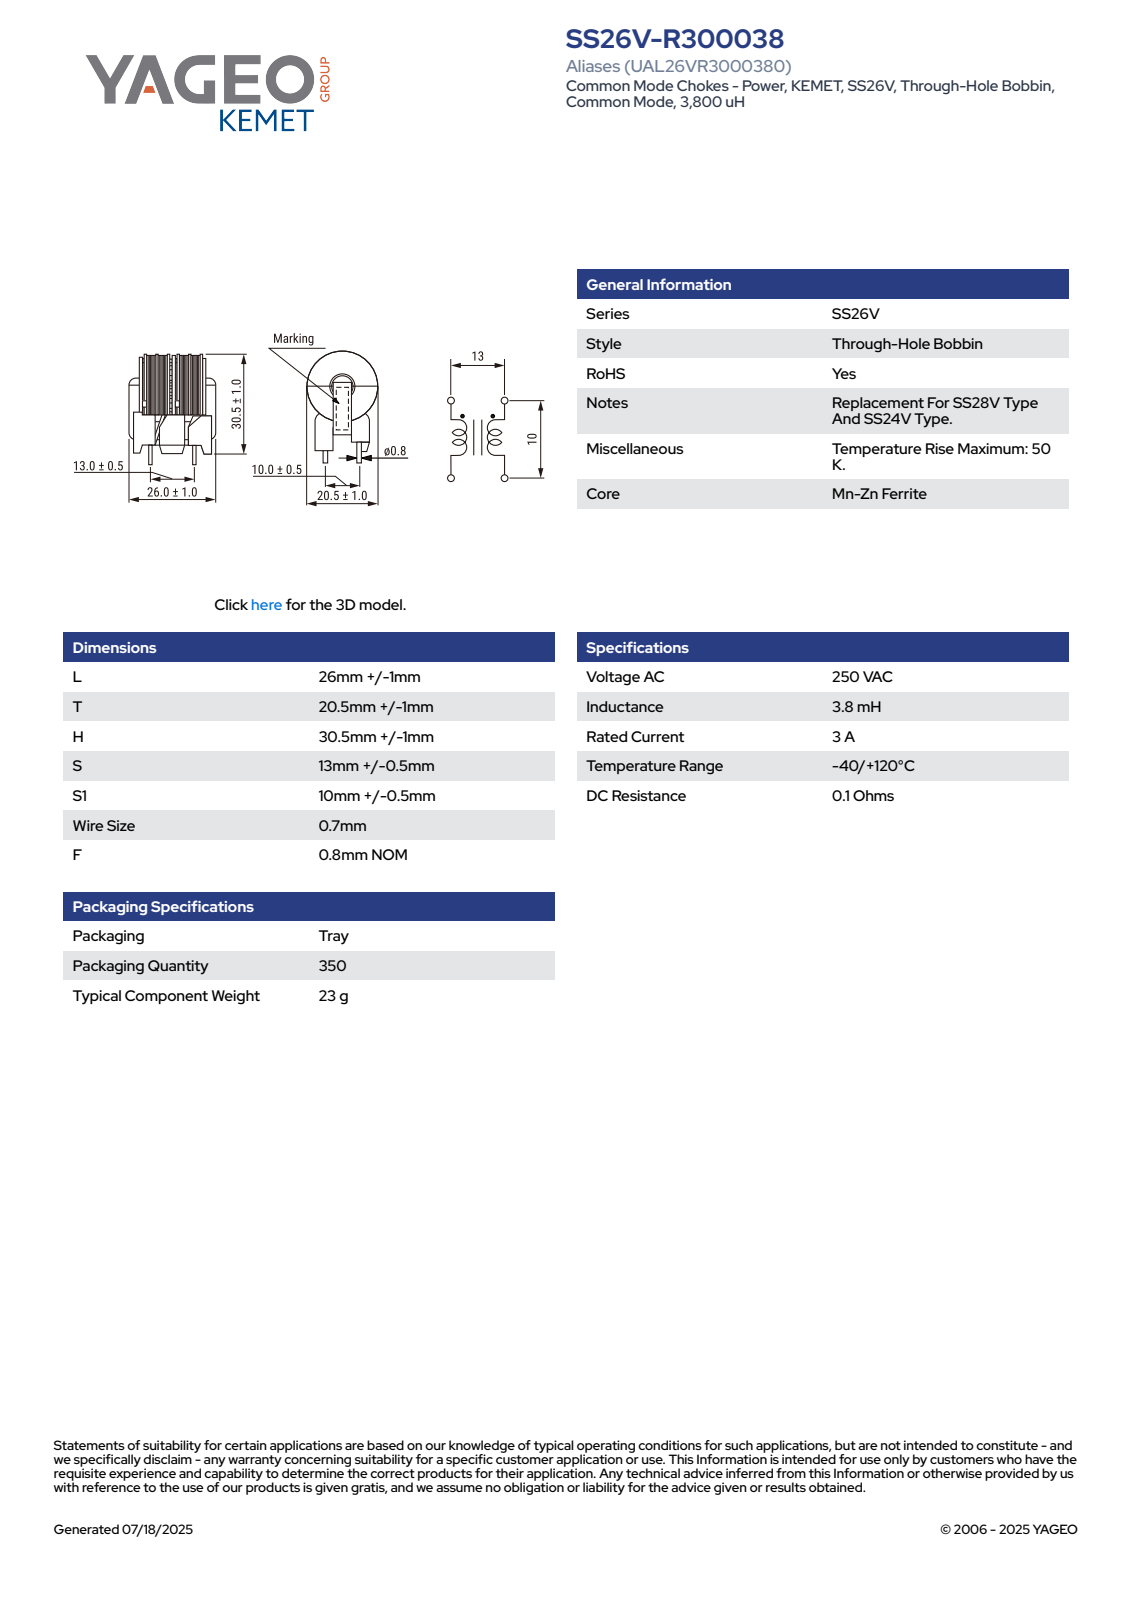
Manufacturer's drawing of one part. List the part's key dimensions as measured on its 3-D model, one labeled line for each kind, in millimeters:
Part name (STEP PRODUCT): SS26V(MAX-LOGO)
STEP written by: SolidWorks 2018 (AUTOMOTIVE_DESIGN)
Units: millimetres
Bodies: 1 solid, 669 faces (259 planar, 202 cylindrical, 208 other)
Overall size (bounding box): 34.45 × 27 × 21.5
Volume: 7 917 mm³ · Surface area: 8 649 mm²
Round holes (diameter × count): ⌀6 ×1, ⌀6.4 ×1
Round bosses / shafts (diameter × count): ⌀0.8 ×4, ⌀21.5 ×1, ⌀19.65 ×1, ⌀15 ×1
Partial cylindrical surfaces — rounded edges, fillets, slot ends (radius × count): R0.5 ×56, R0.2 ×20, R0.3 ×16, R0.8 ×12, R3 ×2, R4 ×1, R4.5 ×1, R8.8 ×1
Main face-to-face distances: 9.65, 0.82, 5.2, 4, 9.63, 0.84, 8.83, 9.67, 10.47, 0.8
